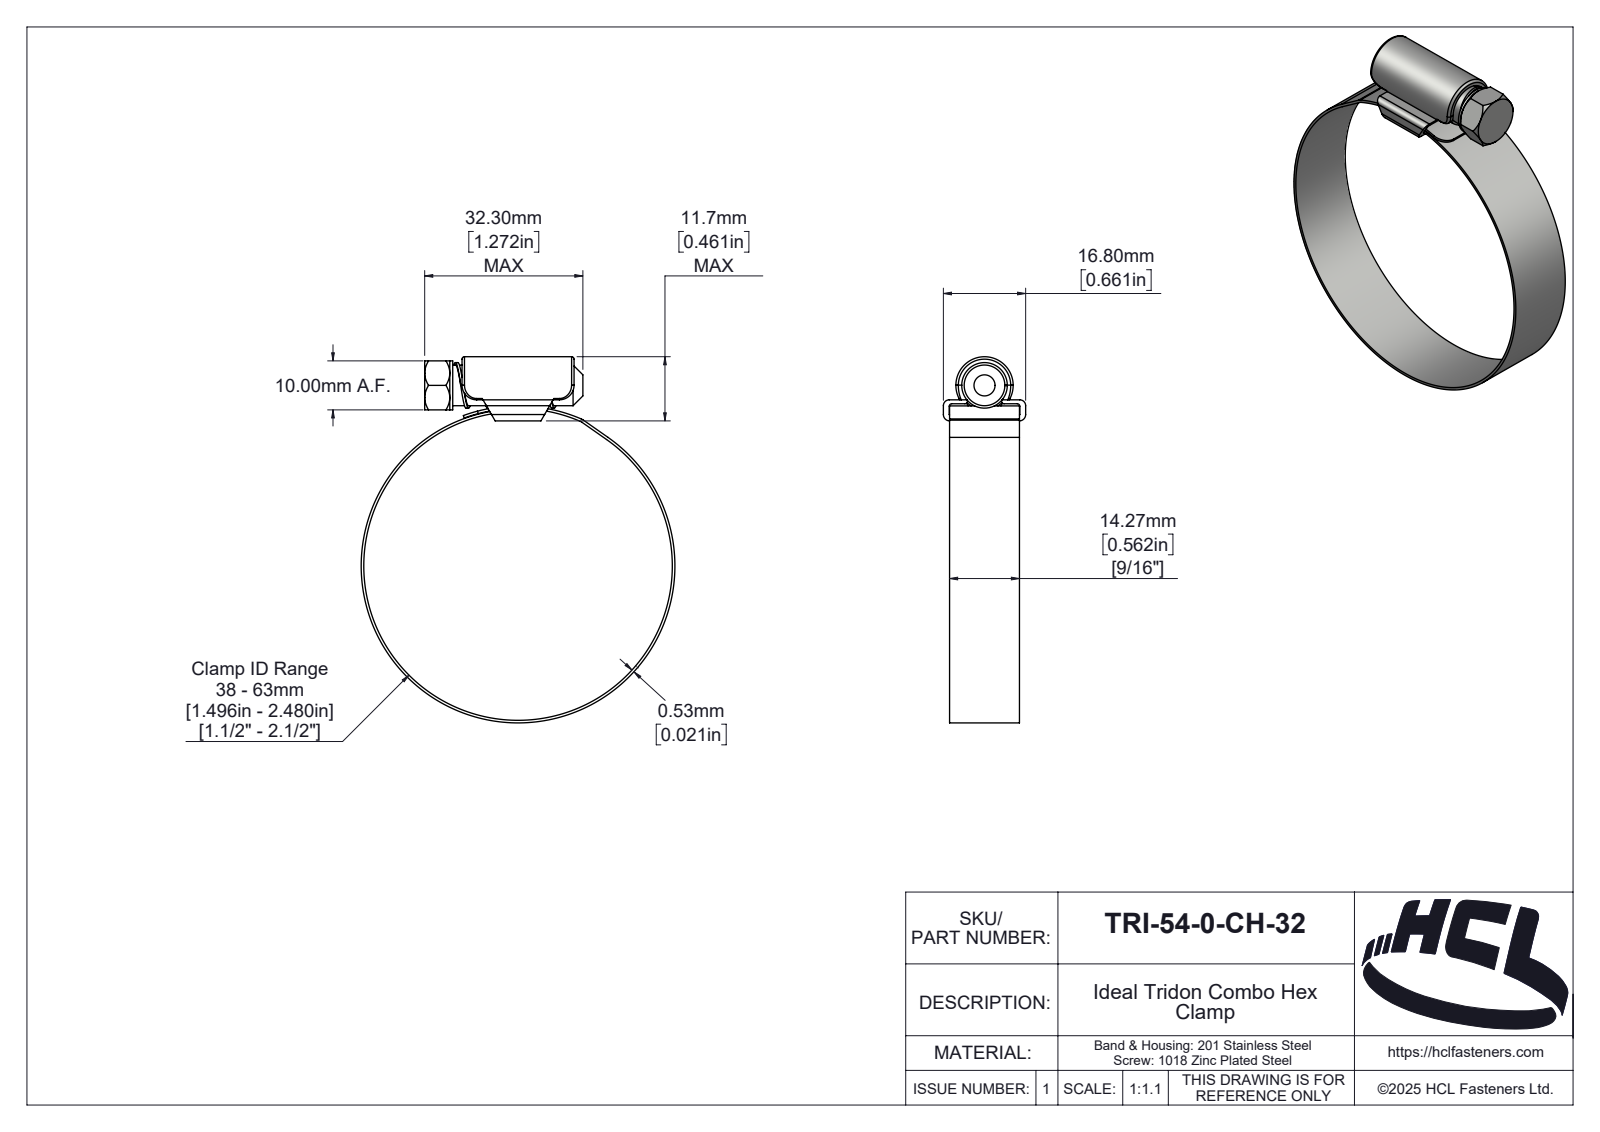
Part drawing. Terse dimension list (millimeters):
name: TRI-54-0-CH-32
written by: SolidWorks 2025 (AUTOMOTIVE_DESIGN)
unit: mm
bodies: 3 solids, 212 faces (35 planar, 101 cylindrical, 76 other)
size: 74.73 × 64.06 × 16.8
volume: 4 482 mm³; area: 9 236 mm²
holes: 1× ⌀63
bosses: 1× ⌀64.06, 1× ⌀10, 1× ⌀8.3
rounds: 6× R0.5, 4× R3, 2× R0.1, 2× R1.2, 2× R1.3, 1× R0.46, 1× R1.89, 1× R2
face distances: 1.2, 14.26, 0.53, 3.5, 2.3, 4.3, 3.1, 0.8, 9.99, 1.27
